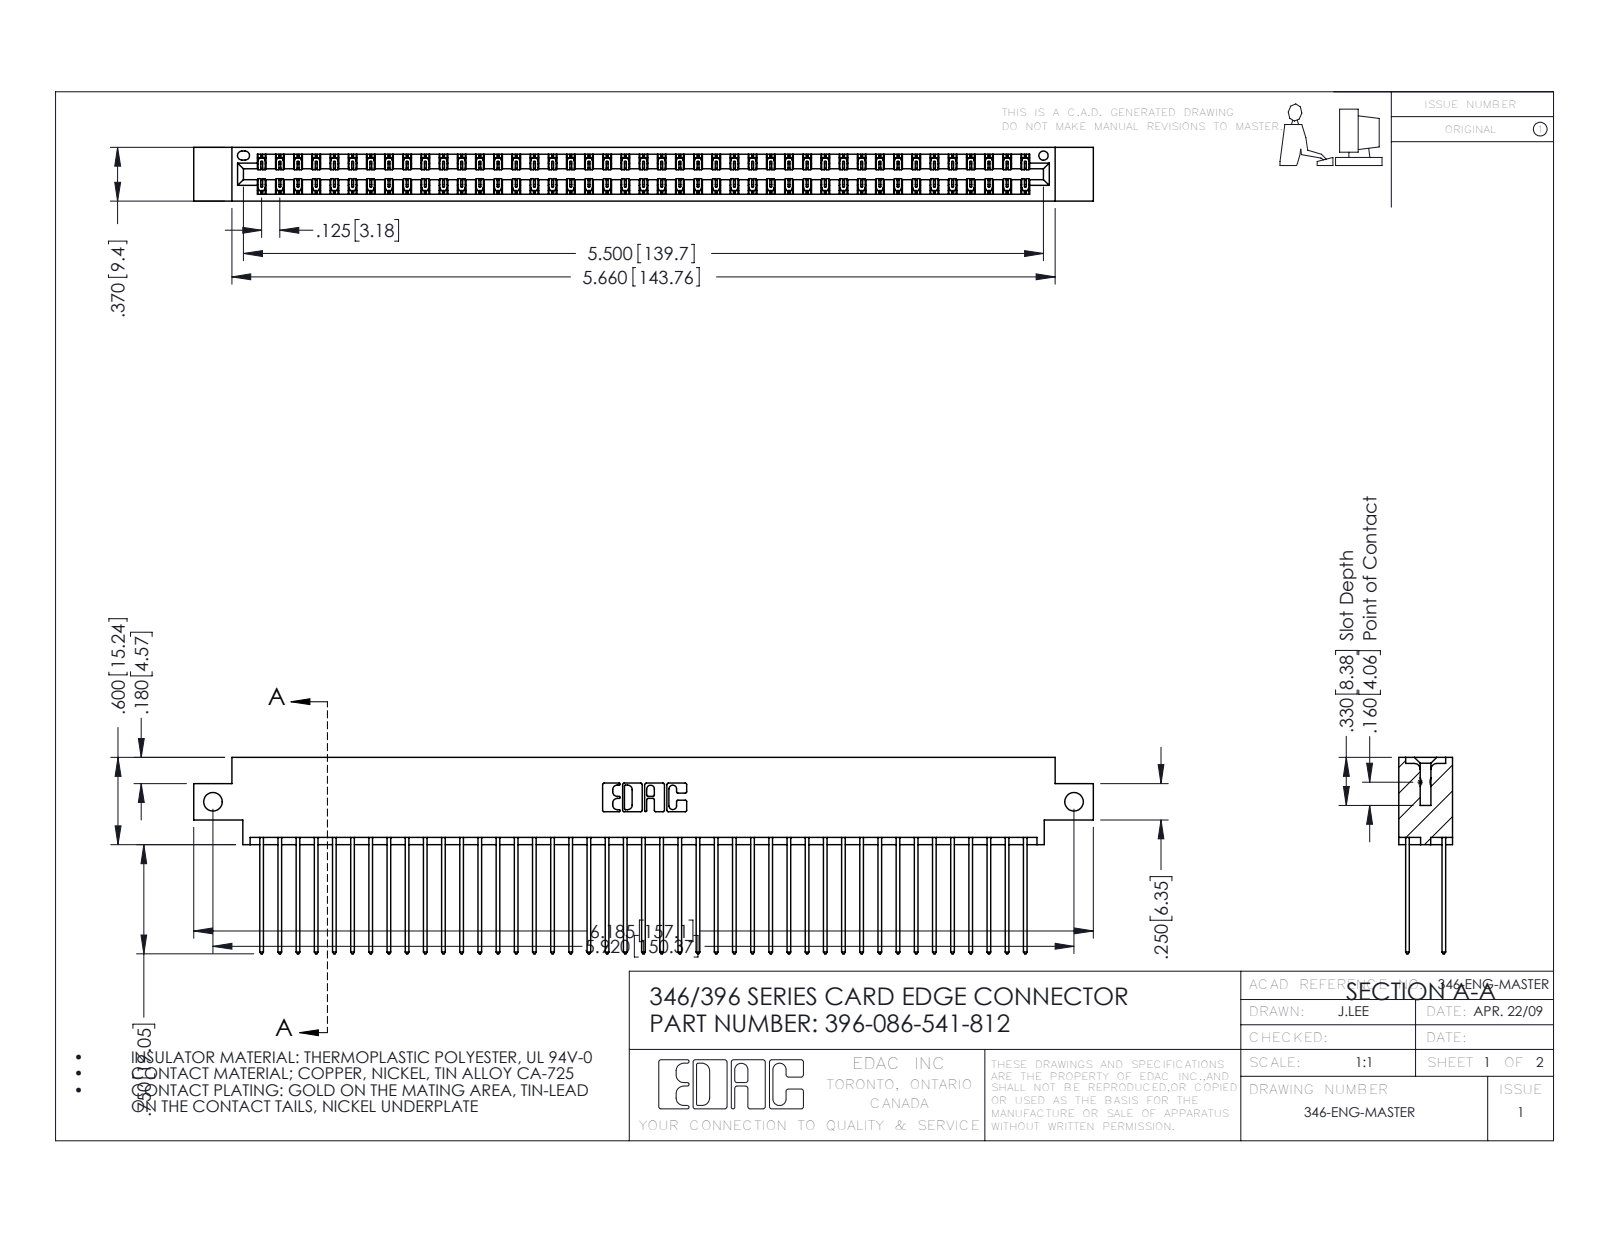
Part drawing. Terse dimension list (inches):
name: 396-086-541-812; 345-292-001_345-293-141; 346 Part_0.170 Offset - Side Mount
written by: SolidWorks 2016 (CONFIG_CONTROL_DESIGN)
unit: in
bodies: 87 solids, 4598 faces (3090 planar, 1508 cylindrical, 0 other)
size: 6.185 × 1.35 × 0.37
volume: 0.951 in³; area: 36.95 in²
holes: 2× ⌀0.128, 1× ⌀0.064
rounds: 129× R0.006, 86× R0.01, 22× R0.01, 6× R0.007, 6× R0.031, 3× R0.026, 2× R0.014, 2× R0.022
face distances: 0.048, 0.322, 0.25, 0.072, 0.298, 0.025, 0.37, 0.275, 0.225, 0.148
hole spacings: 5.92
